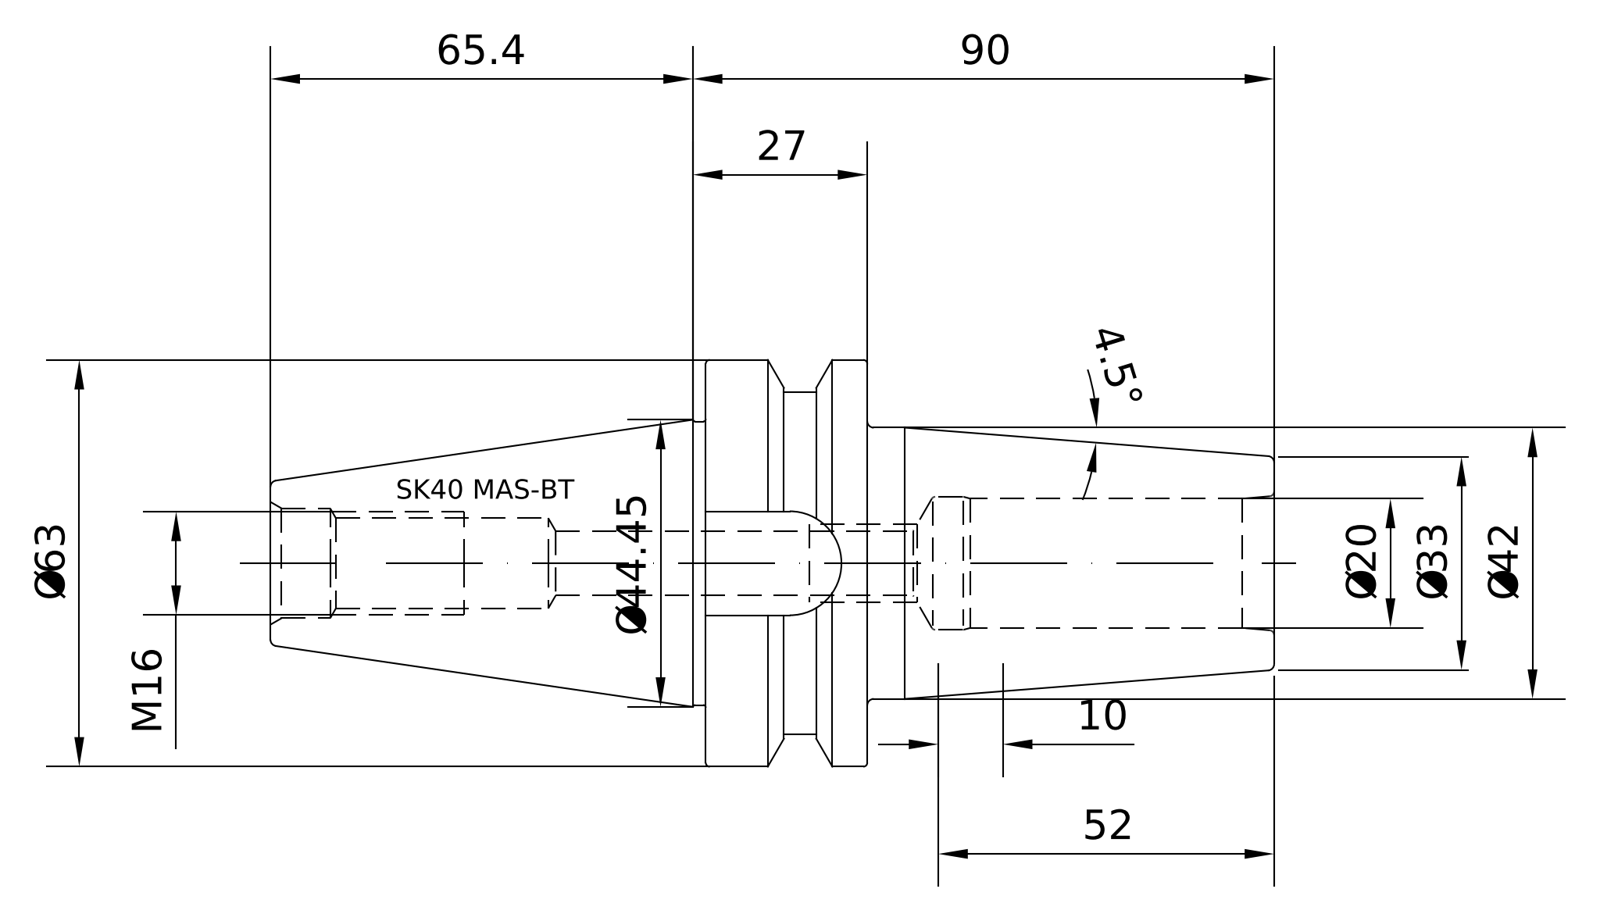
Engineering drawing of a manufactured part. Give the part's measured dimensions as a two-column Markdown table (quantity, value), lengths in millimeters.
| quantity | value |
| --- | --- |
| part name | 40-640-20 |
| STEP written by | PRO/ENGINEER BY PARAMETRIC TECHNOLOGY CORPORATION, 2010430 (CONFIG_CONTROL_DESIGN) |
| units | millimeters |
| bodies | 1 solid, 96 faces (26 planar, 22 cylindrical, 48 other) |
| overall size | 155.4 × 62.98 × 62.98 |
| volume | 181 336 mm³ |
| surface area | 32 002 mm² |
| round holes (diameter × count) | 13.84 × 1, 17.01 × 1, 17.5 × 1, 20 × 1 |
| round bosses / shafts (diameter × count) | 62.98 × 1, 52.75 × 1, 43.75 × 1, 42 × 1, 16.01 × 1 |
| partial cylindrical surfaces (radius × count) | 8.1 × 1 |
| main face-to-face distances | 25, 88, 63, 36, 44.9, 11, 52, 67.4, 16.2, 92.4 |
